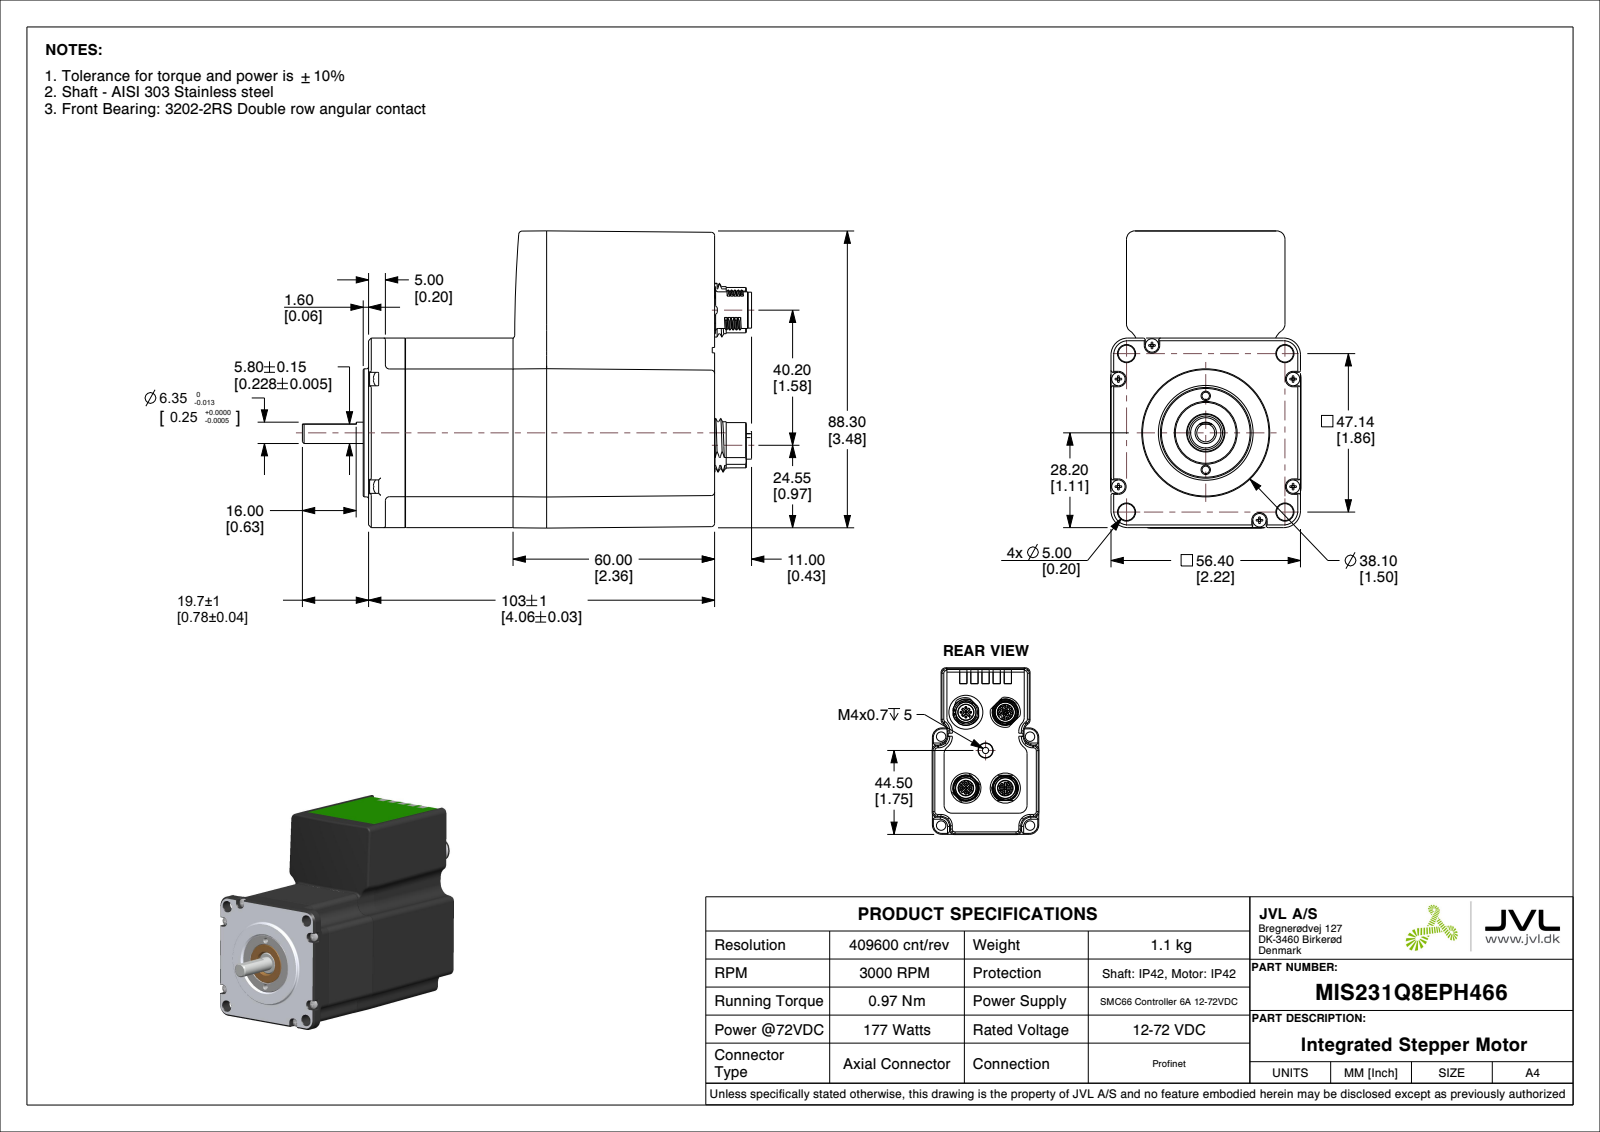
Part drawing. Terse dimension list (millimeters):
name: FRONT_CAP_1; STATOR; AXIAL_CON; SHAFT_1 (+4 more)
written by: CREO PARAMETRIC BY PTC INC, 2018190 (AUTOMOTIVE_DESIGN)
unit: mm
bodies: 13 solids, 1953 faces (767 planar, 563 cylindrical, 623 other)
size: 133.7 × 88.42 × 56.67
volume: 386 026 mm³; area: 57 286 mm²
holes: 27× ⌀1, 6× ⌀2.5, 4× ⌀2, 4× ⌀5, 3× ⌀12.2, 2× ⌀2.2, 2× ⌀11.13, 1× ⌀3.3, 1× ⌀8.3, 1× ⌀10.9, 1× ⌀11, 1× ⌀14
bosses: 6× ⌀4, 5× ⌀1, 3× ⌀14, 3× ⌀13.5, 2× ⌀16, 2× ⌀2, 1× ⌀38.1, 1× ⌀18.1
rounds: 61× R0.2, 29× R2.5, 21× R0.1, 18× R5, 17× R0.6, 16× R1, 12× R0.8, 8× R0.25
face distances: 32, 56.4, 4.75, 91.3, 59.3, 11, 102.3, 43, 39.3, 7.3
hole spacings: 3.54, 7.78, 30, 39.61, 49.53, 62.94, 2.5, 3.25
